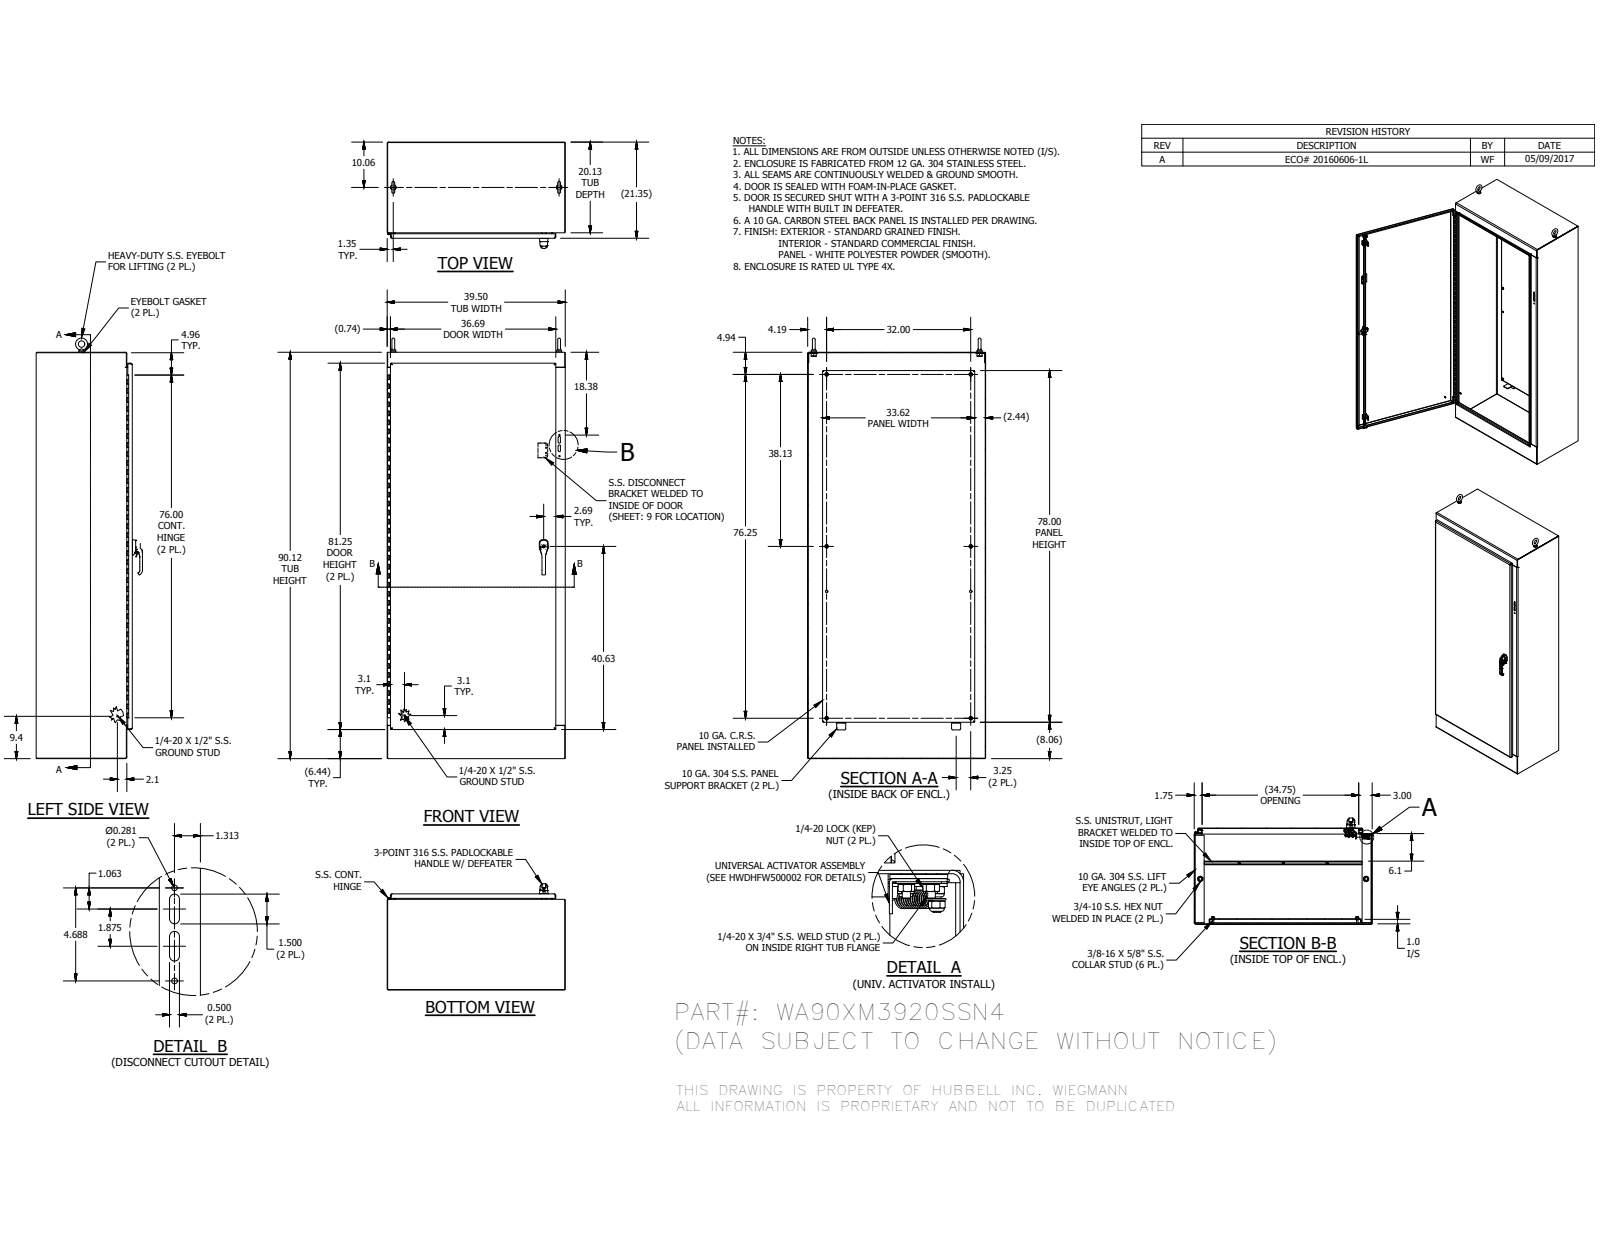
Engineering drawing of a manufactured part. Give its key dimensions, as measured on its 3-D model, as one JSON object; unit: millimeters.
{"part_name": "WA90XM3920SSN4BLS; WAXM3920SSN4TOP; WAXM3920SSN4BTM; FUN00129_WAXM39SSN4 (+8 more)", "step_written_by": "Autodesk Inventor 2016 (AUTOMOTIVE_DESIGN)", "units": "millimeters", "bodies": {"solids": 127, "faces": 4880, "planar": 2278, "cylindrical": 1560, "other": 1042}, "overall_size": [2368.49, 1003.3, 599.35], "volume_mm3": 30450000, "surface_area_mm2": 21650000, "round_holes": [[3.55, 24], [9.52, 10], [6.35, 9], [6.65, 8], [14.29, 8], [3.96, 6], [7.8, 6], [4.76, 5], [3.45, 4], [4.17, 4], [5.1, 4], [7.37, 4]], "round_bosses_or_shafts": [[15.88, 10], [8.38, 9], [14.29, 6], [13.54, 4], [8.56, 4], [6.35, 4], [6.02, 4], [6, 3]], "partial_cylinders_radius": [[0.5, 187], [0.3, 109], [0.51, 48], [6.35, 25], [0.47, 21], [1.59, 20], [3.17, 18], [0.64, 16]], "face_to_face_distances": [2.64, 539.59, 1000.66, 536.95, 542.23, 3.41, 25.4, 514.19, 31.45, 28.81], "hole_center_spacings": [0.45, 214.49, 1830.75, 0.59, 0.6, 0.74, 9.65, 19.31]}
